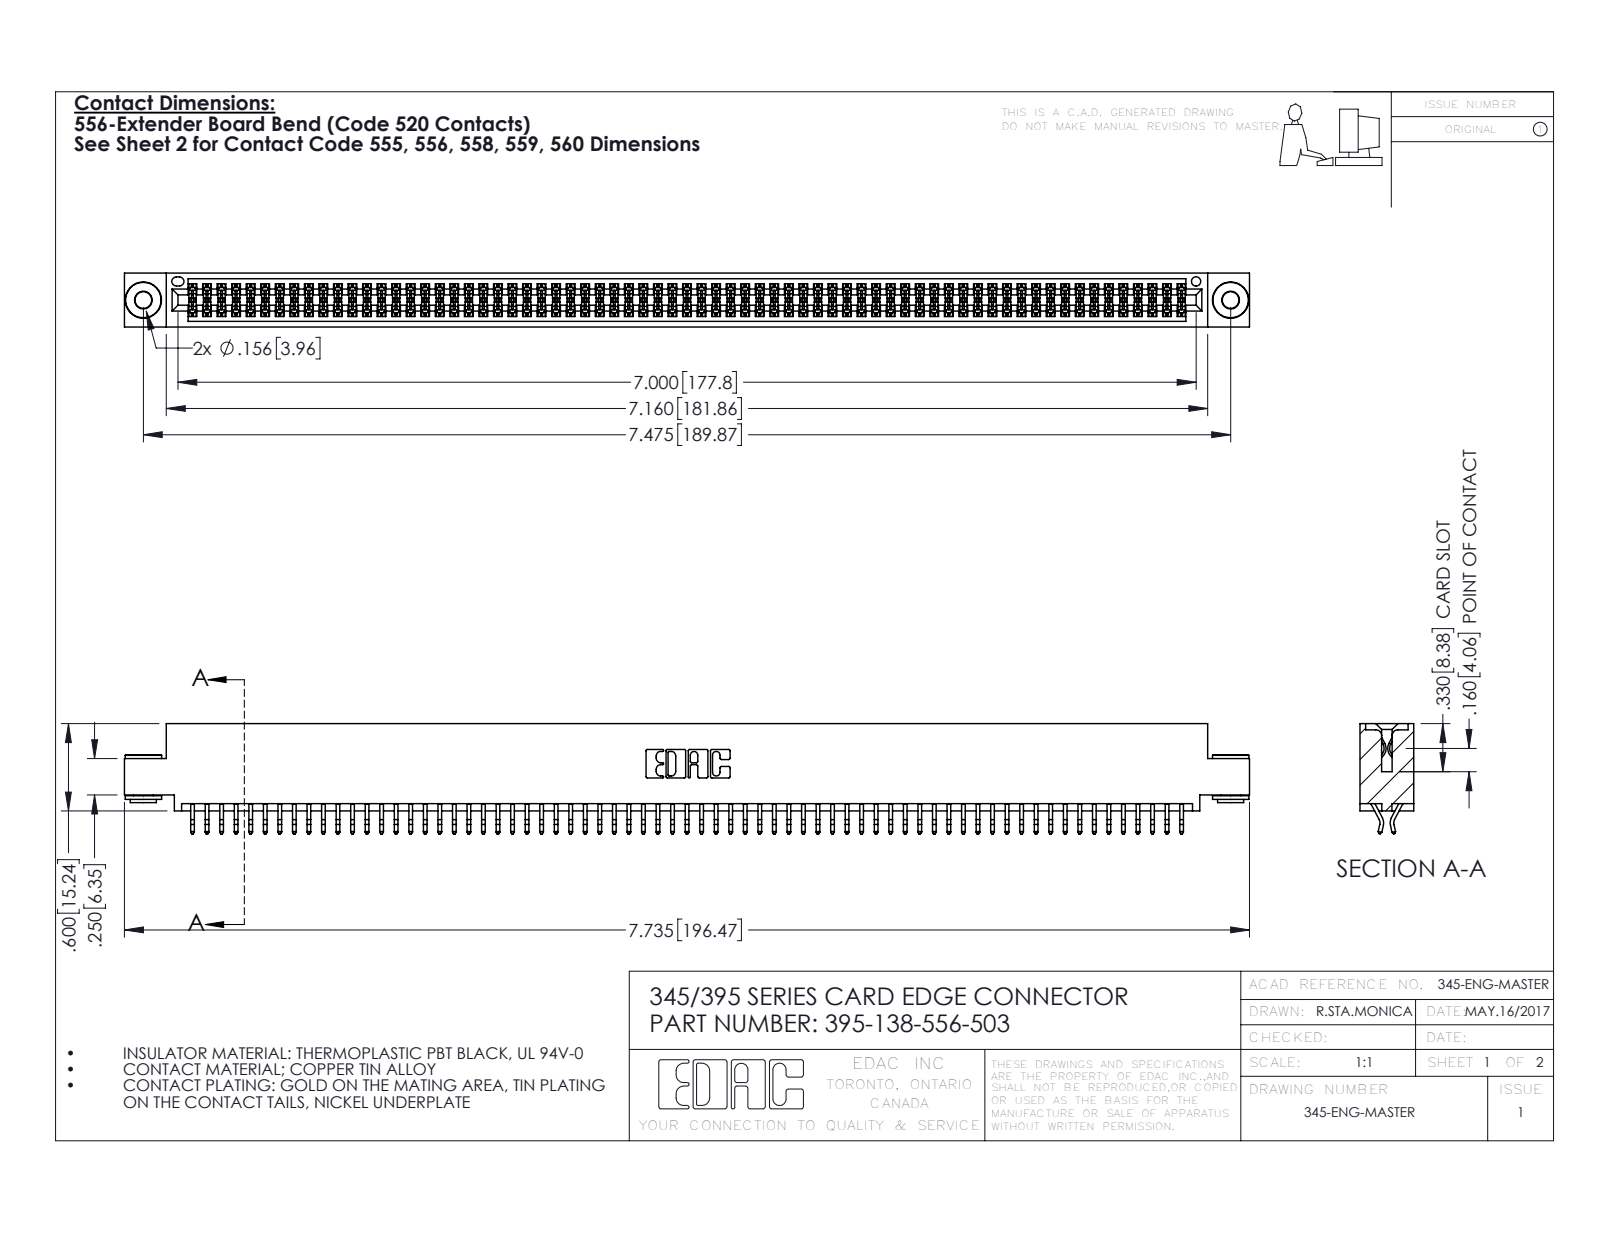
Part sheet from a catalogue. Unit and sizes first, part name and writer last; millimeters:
Units: millimetres
Overall size (bounding box): 196.5 × 19.2 × 9.4
Round holes (diameter × count): ⌀2.9 ×2, ⌀4 ×2, ⌀1.6 ×1
Round bosses / shafts (diameter × count): ⌀6.4 ×2, ⌀4.6 ×2, ⌀3.5 ×2
Partial cylindrical surfaces — rounded edges, fillets, slot ends (radius × count): R0.2 ×207, R0.3 ×22, R0.2 ×6, R0.8 ×6, R0.7 ×3, R0.3 ×2, R0.4 ×2, R0.5 ×2
Main face-to-face distances: 1.8, 7.6, 9.4, 5.1, 0.6, 2.5, 6.9, 5.7, 4.4, 3.8
Hole centre spacings: 6.9, 183.9, 189.9
Volume: 19 270 mm³ · Surface area: 29 190 mm²
Bodies: 141 solids, 7896 faces (5200 planar, 2688 cylindrical, 8 other)
Part name (STEP PRODUCT): 395-138-556-503; 345-250-002_345-250-002-102; 345-292-001_556 Tail; 345 Part_0.110 Offset - 0.156 Dia-TH
STEP written by: SolidWorks 2016 (CONFIG_CONTROL_DESIGN)
